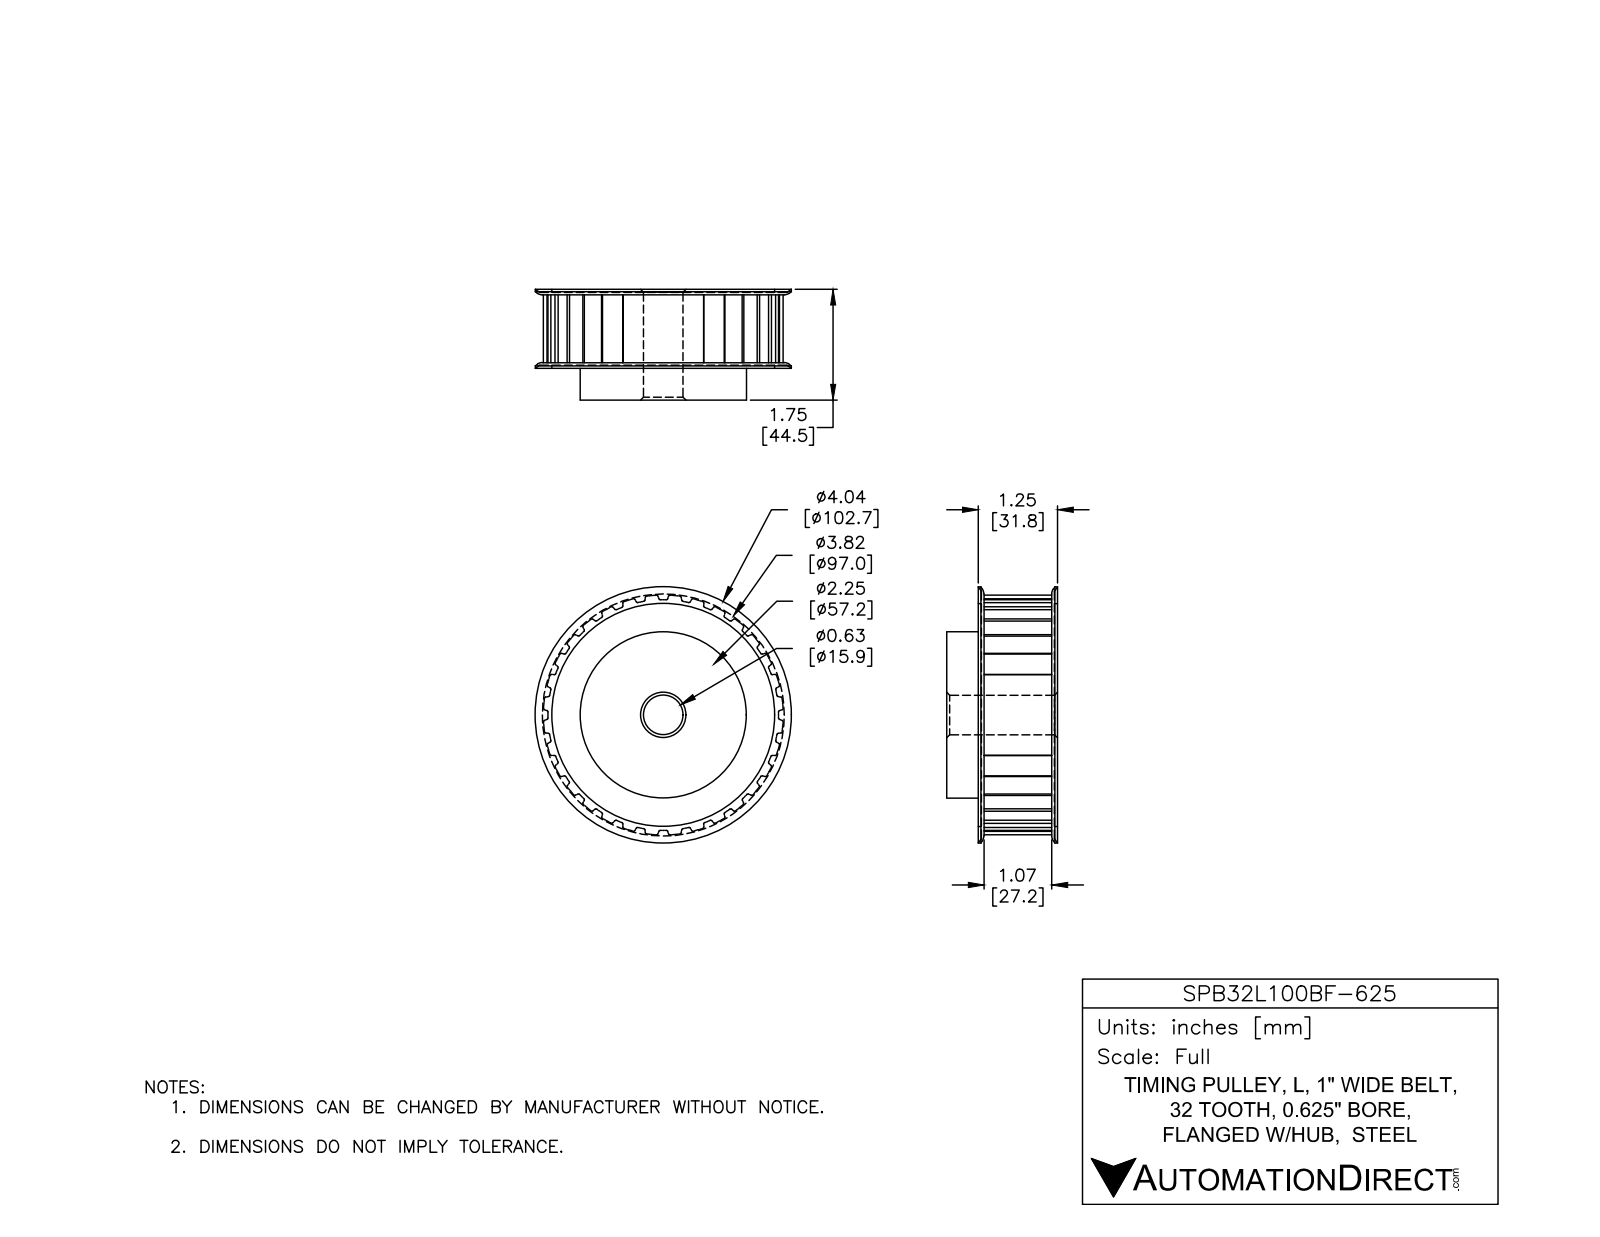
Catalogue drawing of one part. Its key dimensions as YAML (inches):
part_name: "SPB32L100BF-625"
step_written_by: "SolidWorks 2015 (AUTOMOTIVE_DESIGN)"
units: inches
bodies: {solids: 1, faces: 317, planar: 103, cylindrical: 198, other: 16}
overall_size: [4.044, 4.044, 1.75]
volume: 15.84
surface_area: 54.95
round_holes:
  - {diameter: 0.625, count: 1}
round_bosses_or_shafts:
  - {diameter: 4.044, count: 1}
  - {diameter: 3.518, count: 1}
  - {diameter: 2.625, count: 1}
partial_cylinders:
  - {radius: 0.02, count: 128}
  - {radius: 1.895, count: 1}
face_to_face_distances: [1.75, 0.05, 1.2, 1.25, 0.5, 0.55, 1.15, 1.7, 0.09, 1.16]
